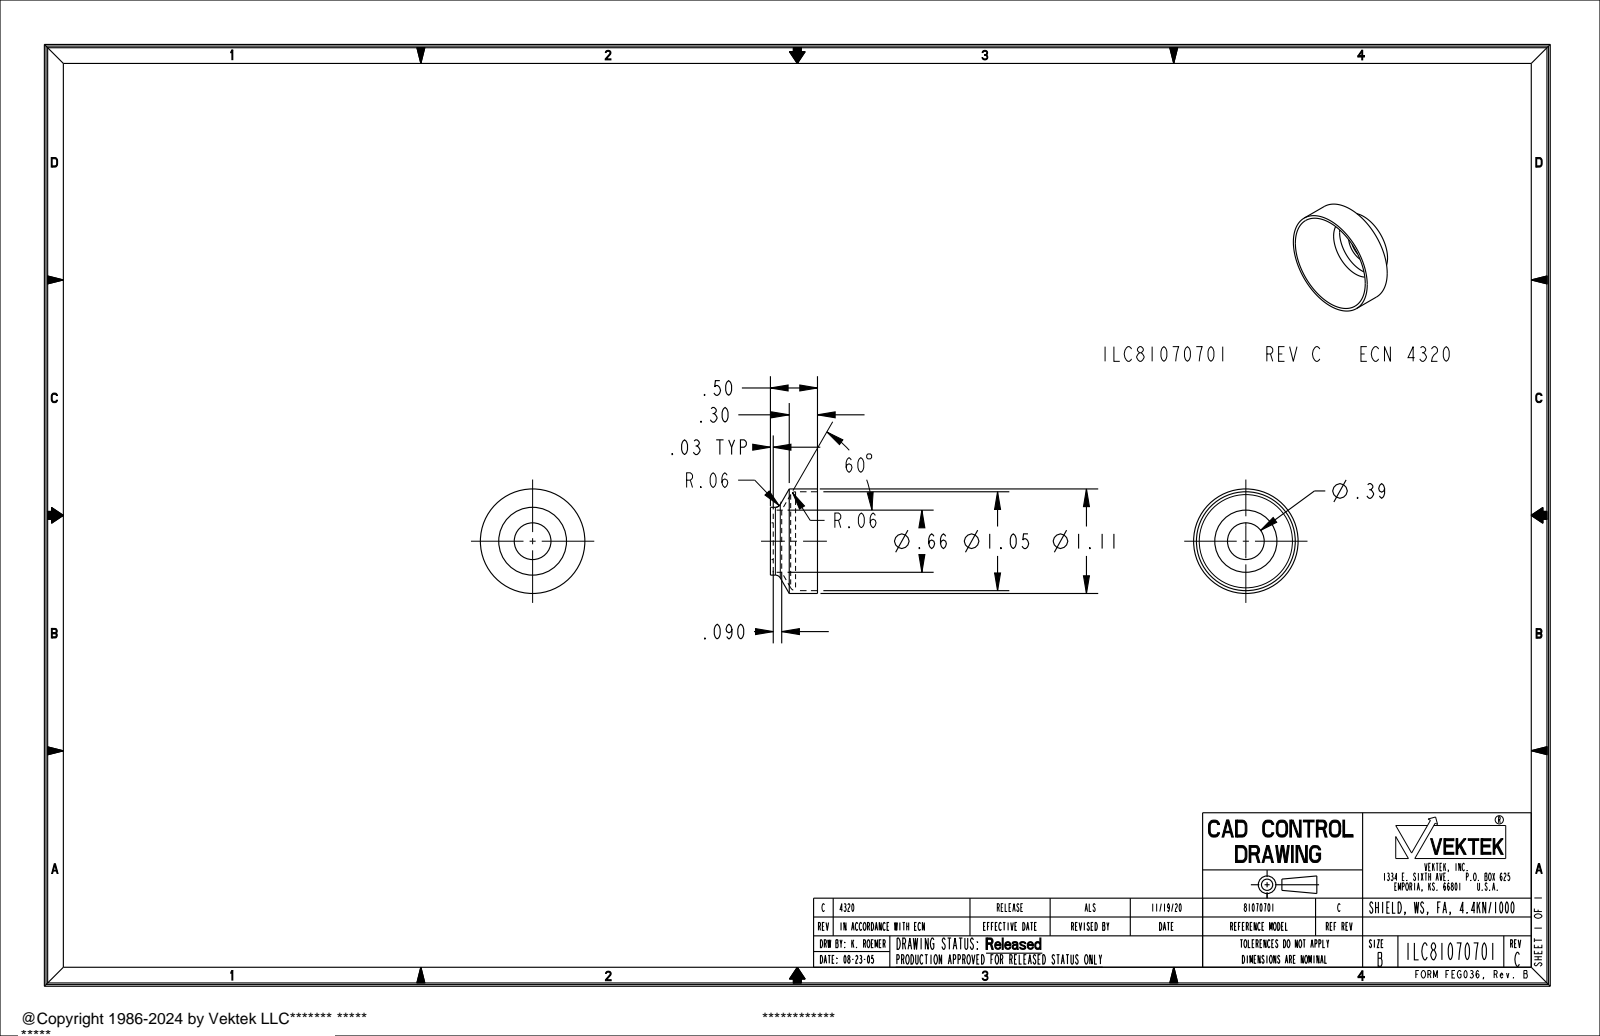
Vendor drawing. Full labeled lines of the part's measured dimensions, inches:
Part name (STEP PRODUCT): ILC81070701
STEP written by: PRO/ENGINEER BY PARAMETRIC TECHNOLOGY CORPORATION, 2013320 (CONFIG_CONTROL_DESIGN)
Units: inches
Bodies: 1 solid, 21 faces (3 planar, 10 cylindrical, 8 other)
Overall size (bounding box): 1.11 × 1.11 × 0.5
Volume: 0.07 in³ · Surface area: 4.178 in²
Round holes (diameter × count): ⌀0.39 ×1, ⌀0.66 ×1, ⌀1.05 ×1
Round bosses / shafts (diameter × count): ⌀1.11 ×1, ⌀0.72 ×1
Main face-to-face distances: 0.03, 0.5, 0.47
